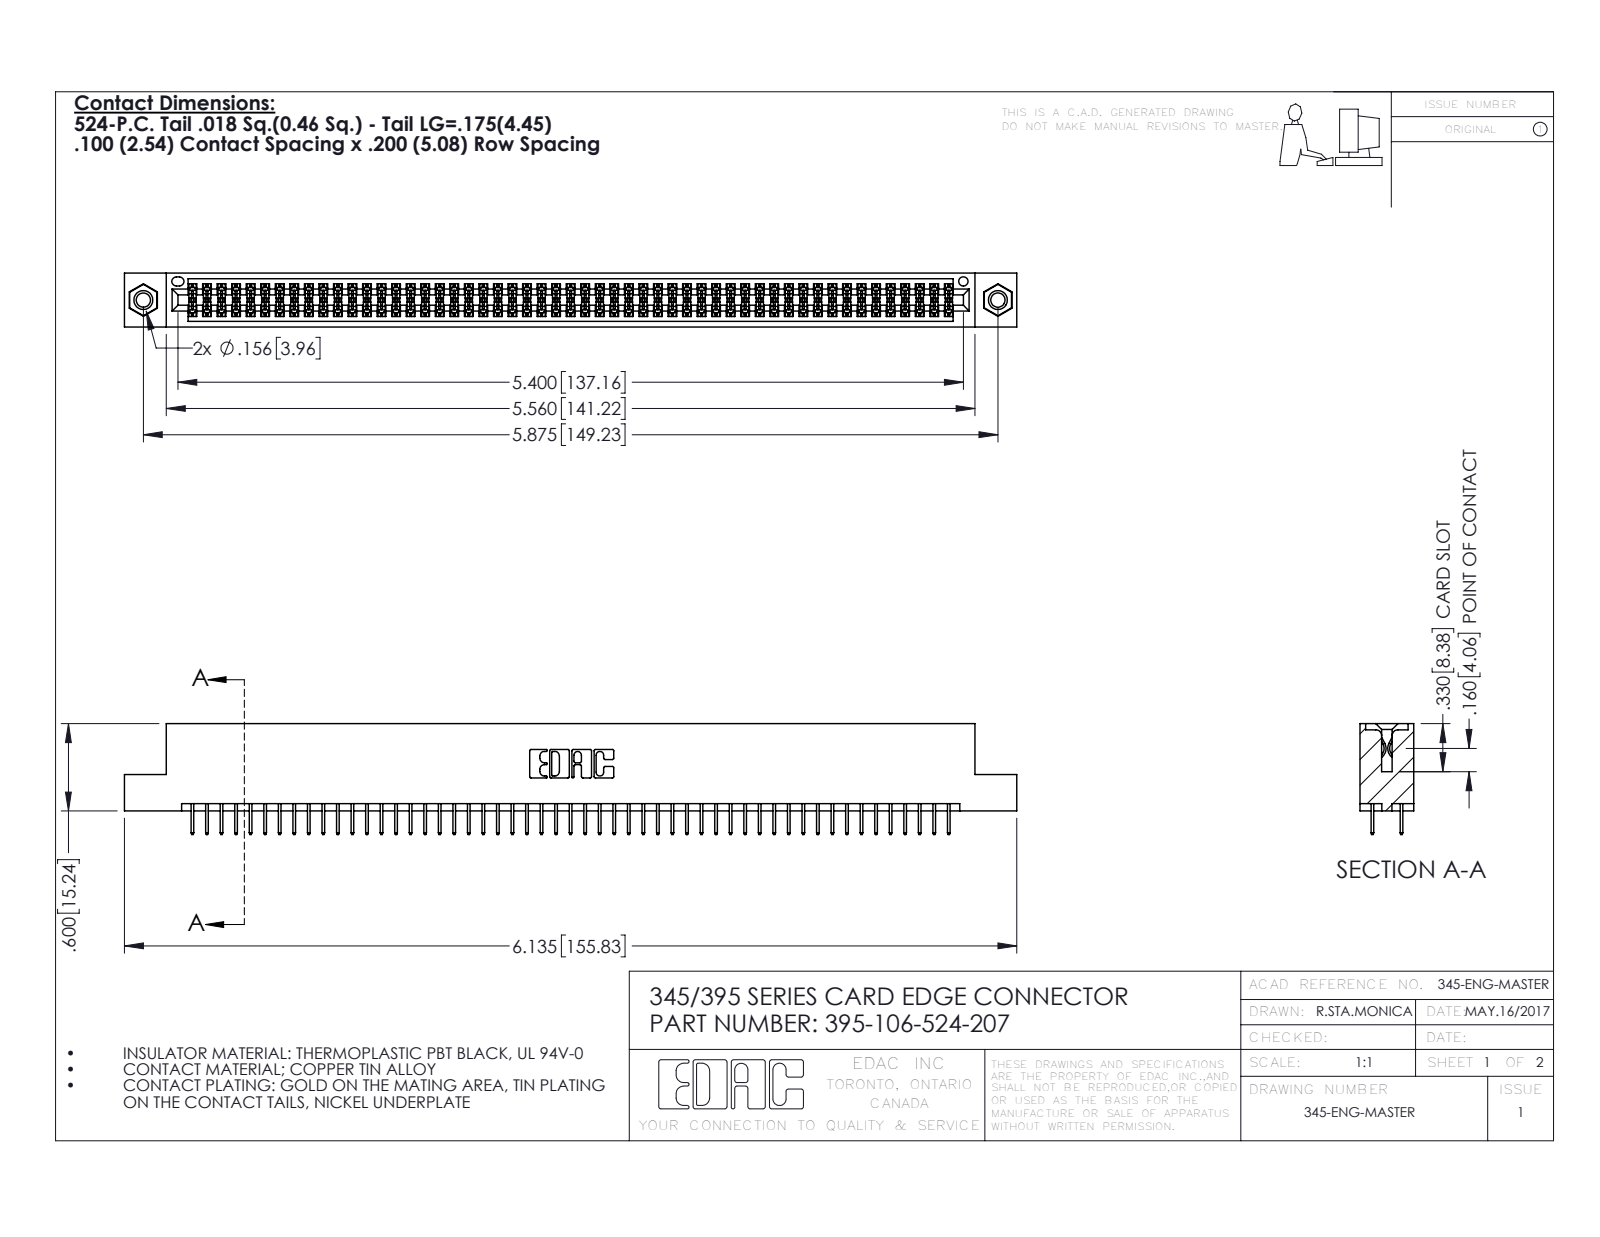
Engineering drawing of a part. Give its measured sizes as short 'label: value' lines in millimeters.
name: 345-250-001_345-250-005-103; 345-292-001_345-293-124; 345 Part_Flush Mounting Lugs - 0.156 Dia-TI; 395-106-524-207
written by: SolidWorks 2016 (CONFIG_CONTROL_DESIGN)
unit: mm
bodies: 109 solids, 5910 faces (4246 planar, 1648 cylindrical, 16 other)
size: 155.8 × 19.4 × 9.4
volume: 15 100 mm³; area: 22 080 mm²
holes: 2× ⌀2.5, 2× ⌀3.2, 2× ⌀4, 1× ⌀1.6
bosses: 2× ⌀3.9
rounds: 159× R0.2, 22× R0.3, 6× R0.2, 6× R0.8, 3× R0.7, 2× R0.4, 2× R0.5, 2× R0.6
face distances: 1.8, 7.6, 5.1, 9.4, 2.5, 6.9, 0.6, 5.7, 1.8, 4.4
hole spacings: 6.9, 143.2, 149.2
